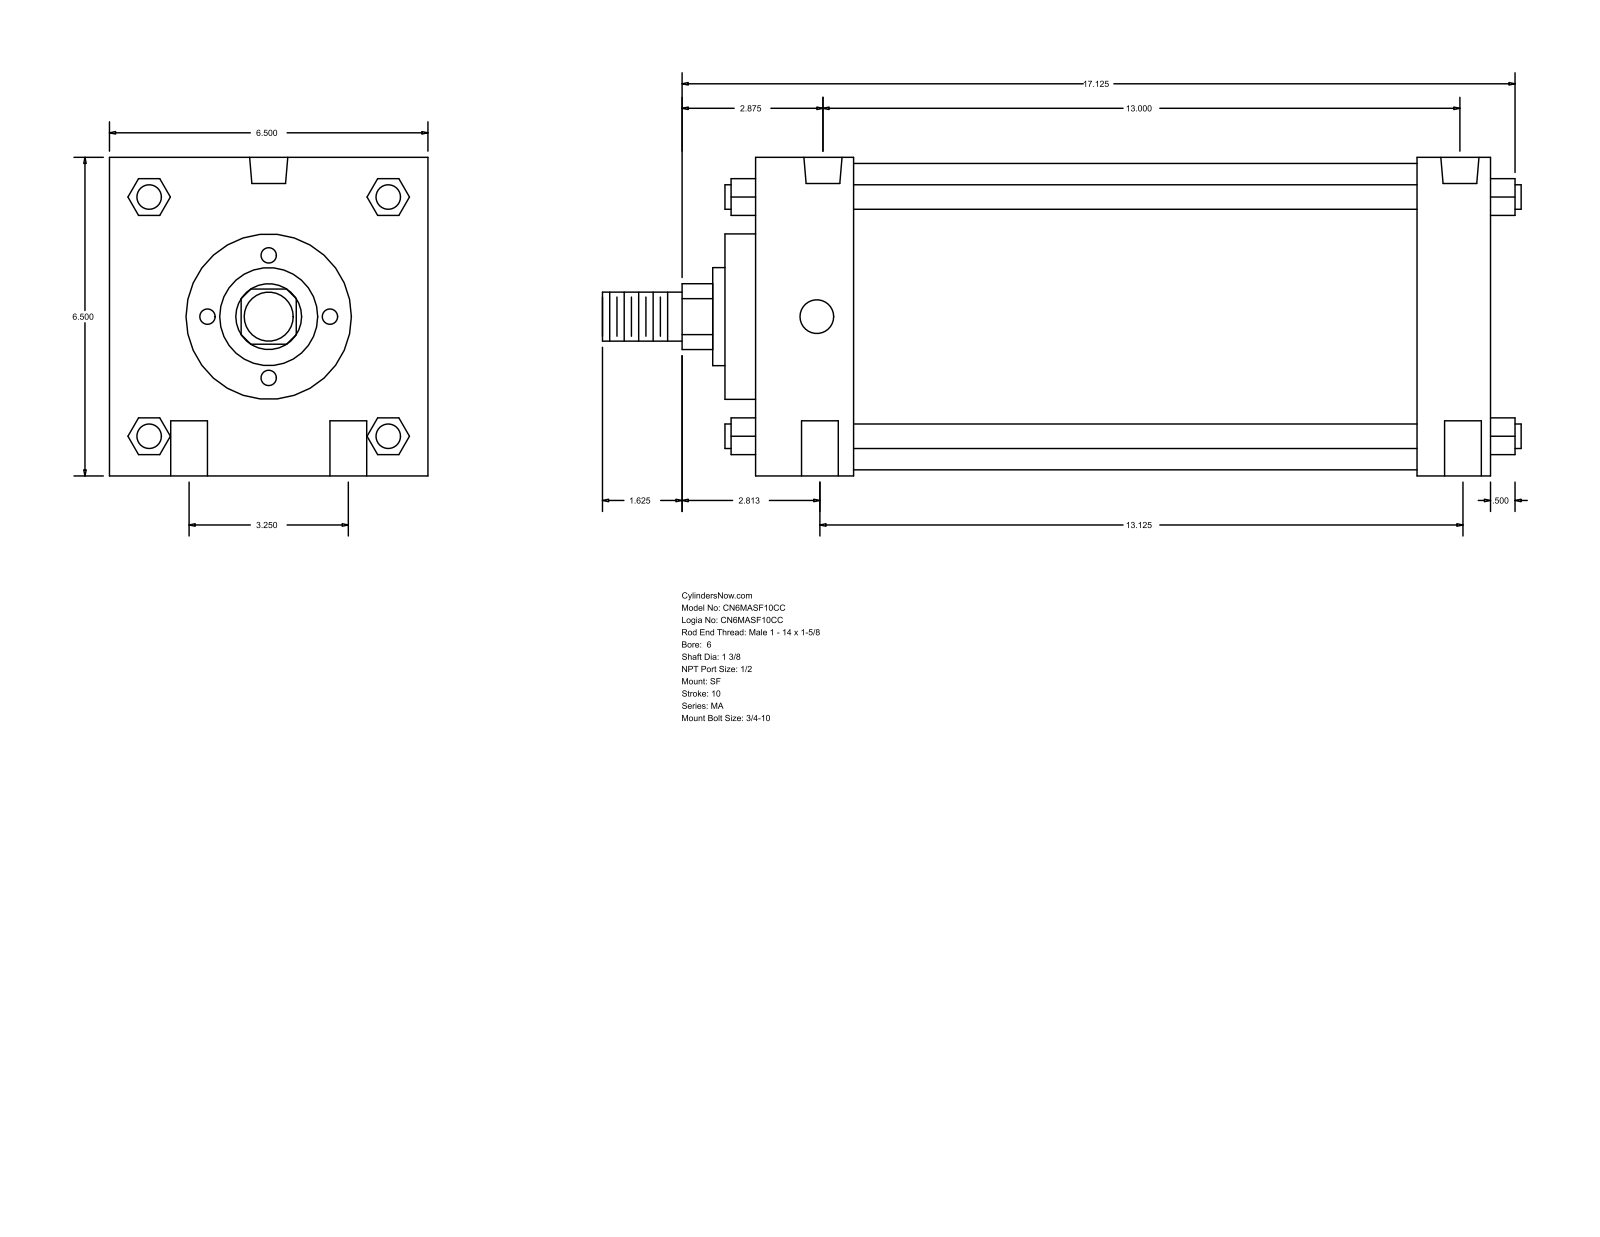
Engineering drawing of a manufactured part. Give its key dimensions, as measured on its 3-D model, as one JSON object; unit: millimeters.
{"part_name": "MA_SF__0600_1.375", "step_written_by": "GSSL Pune (CONFIG_CONTROL_DESIGN)", "units": "millimeters", "bodies": {"solids": 0, "faces": 126, "planar": 95, "cylindrical": 31, "other": 0}, "overall_size": [476.25, 165.1, 165.1], "round_holes": [[19.05, 4], [17.46, 2], [19.77, 2]], "round_bosses_or_shafts": [[12.7, 4], [158.75, 1], [85.72, 1], [50.8, 1], [34.92, 1], [25.4, 1]], "partial_cylinders_radius": [[17.06, 1]], "face_to_face_distances": [165.1, 381, 342.9, 50.8, 38.1, 292.1, 330.2, 66.67, 15.87, 358.77], "hole_center_spacings": [41.3, 82.54, 330.2, 333.37, 334.34, 334.35, 343.44]}
